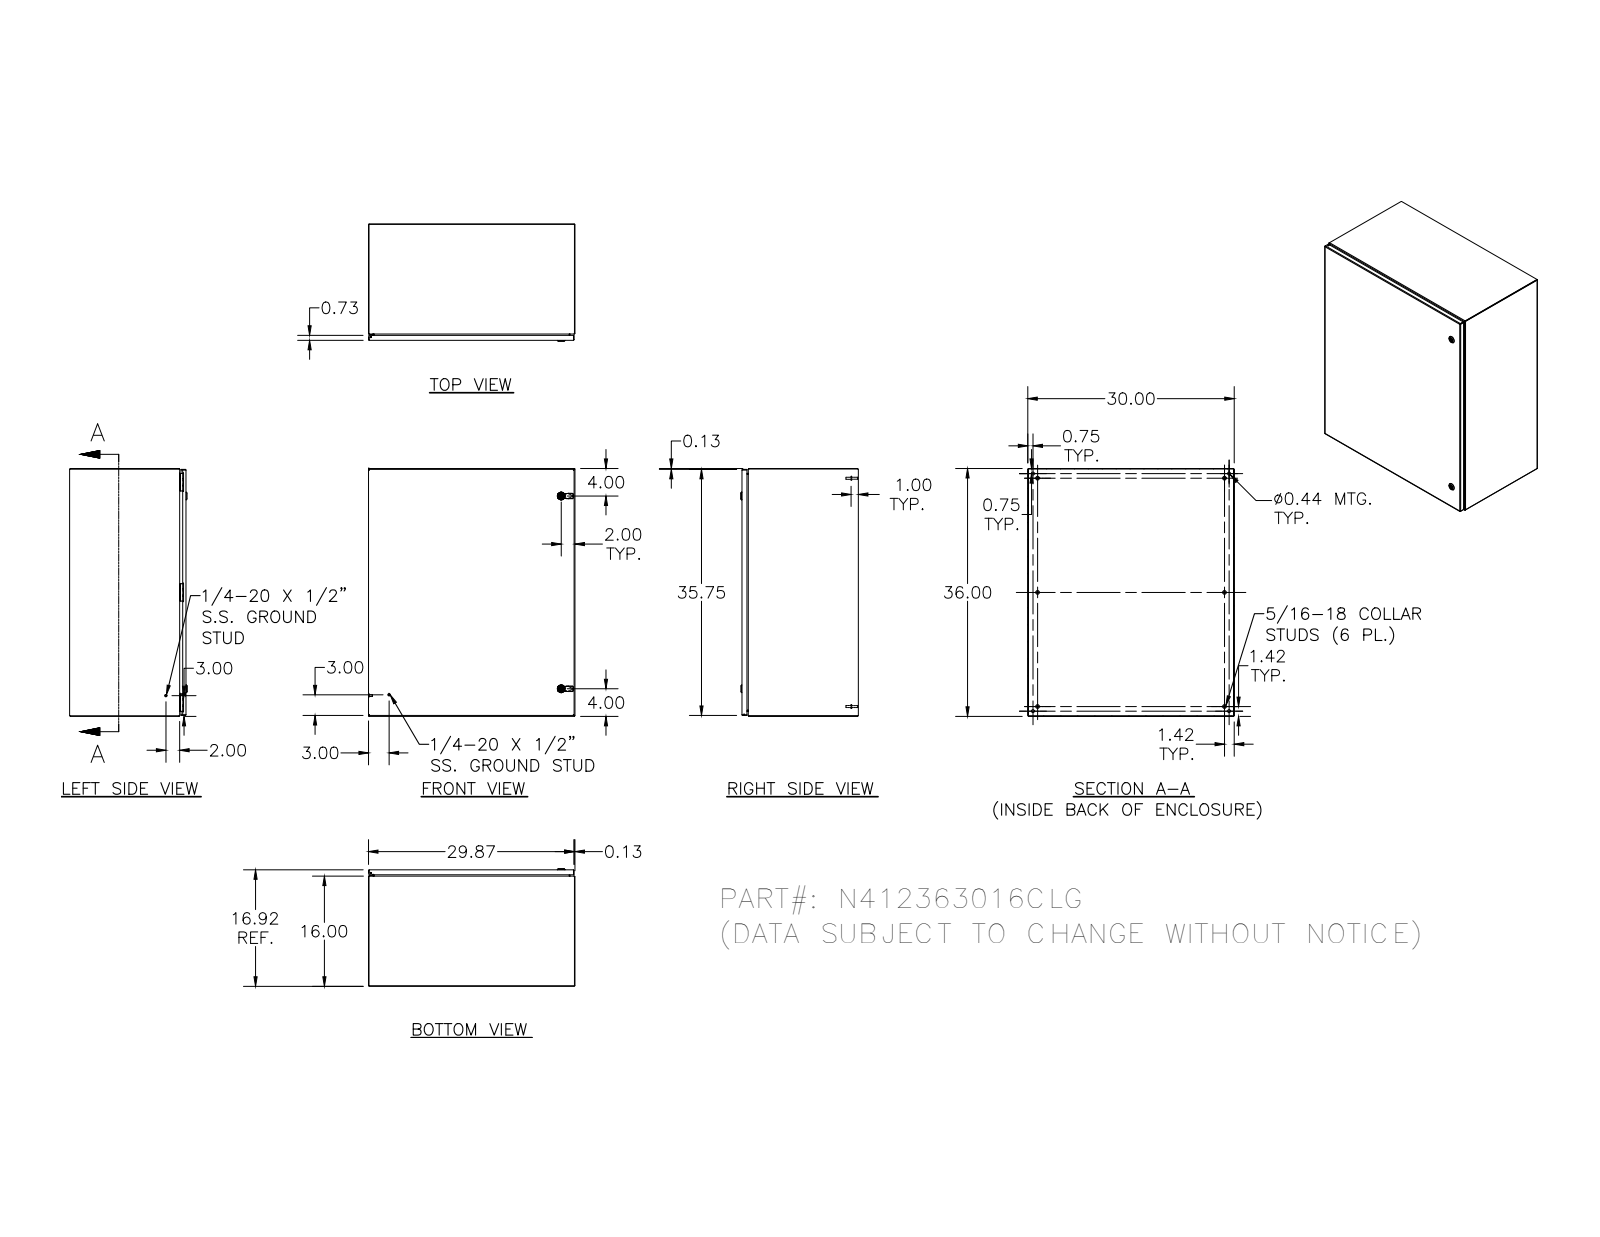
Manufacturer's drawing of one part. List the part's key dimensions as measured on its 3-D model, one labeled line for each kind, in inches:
Part name (STEP PRODUCT): N412363016C; N412363016CBLR; N4123016CTB; N4123630CLID (+8 more)
STEP written by: Autodesk Inventor 2011 (AUTOMOTIVE_DESIGN)
Units: inches
Bodies: 51 solids, 2258 faces (861 planar, 840 cylindrical, 557 other)
Overall size (bounding box): 36 × 30 × 17.075
Volume: 335.4 in³ · Surface area: 9 121 in²
Round holes (diameter × count): ⌀0.188 ×7, ⌀0.093 ×6, ⌀0.152 ×6, ⌀0.167 ×6, ⌀0.172 ×6, ⌀0.438 ×4, ⌀0.156 ×3, ⌀0.197 ×2, ⌀0.315 ×2, ⌀0.394 ×2, ⌀0.402 ×2, ⌀0.634 ×2
Round bosses / shafts (diameter × count): ⌀0.25 ×14, ⌀0.563 ×6, ⌀0.36 ×6, ⌀0.32 ×6, ⌀0.3 ×6, ⌀0.275 ×6, ⌀0.256 ×6, ⌀0.164 ×6
Partial cylindrical surfaces — rounded edges, fillets, slot ends (radius × count): R0.012 ×54, R0.05 ×38, R0.031 ×32, R0.016 ×26, R0.125 ×24, R0.02 ×23, R0.105 ×18, R0.032 ×12
Main face-to-face distances: 0.074, 16.843, 29.926, 16.769, 16.917, 35.926, 29.852, 30, 35.852, 36
Hole centre spacings: 16, 16.004, 32.004, 0.5, 0.656, 0.66, 15.344, 0.984
